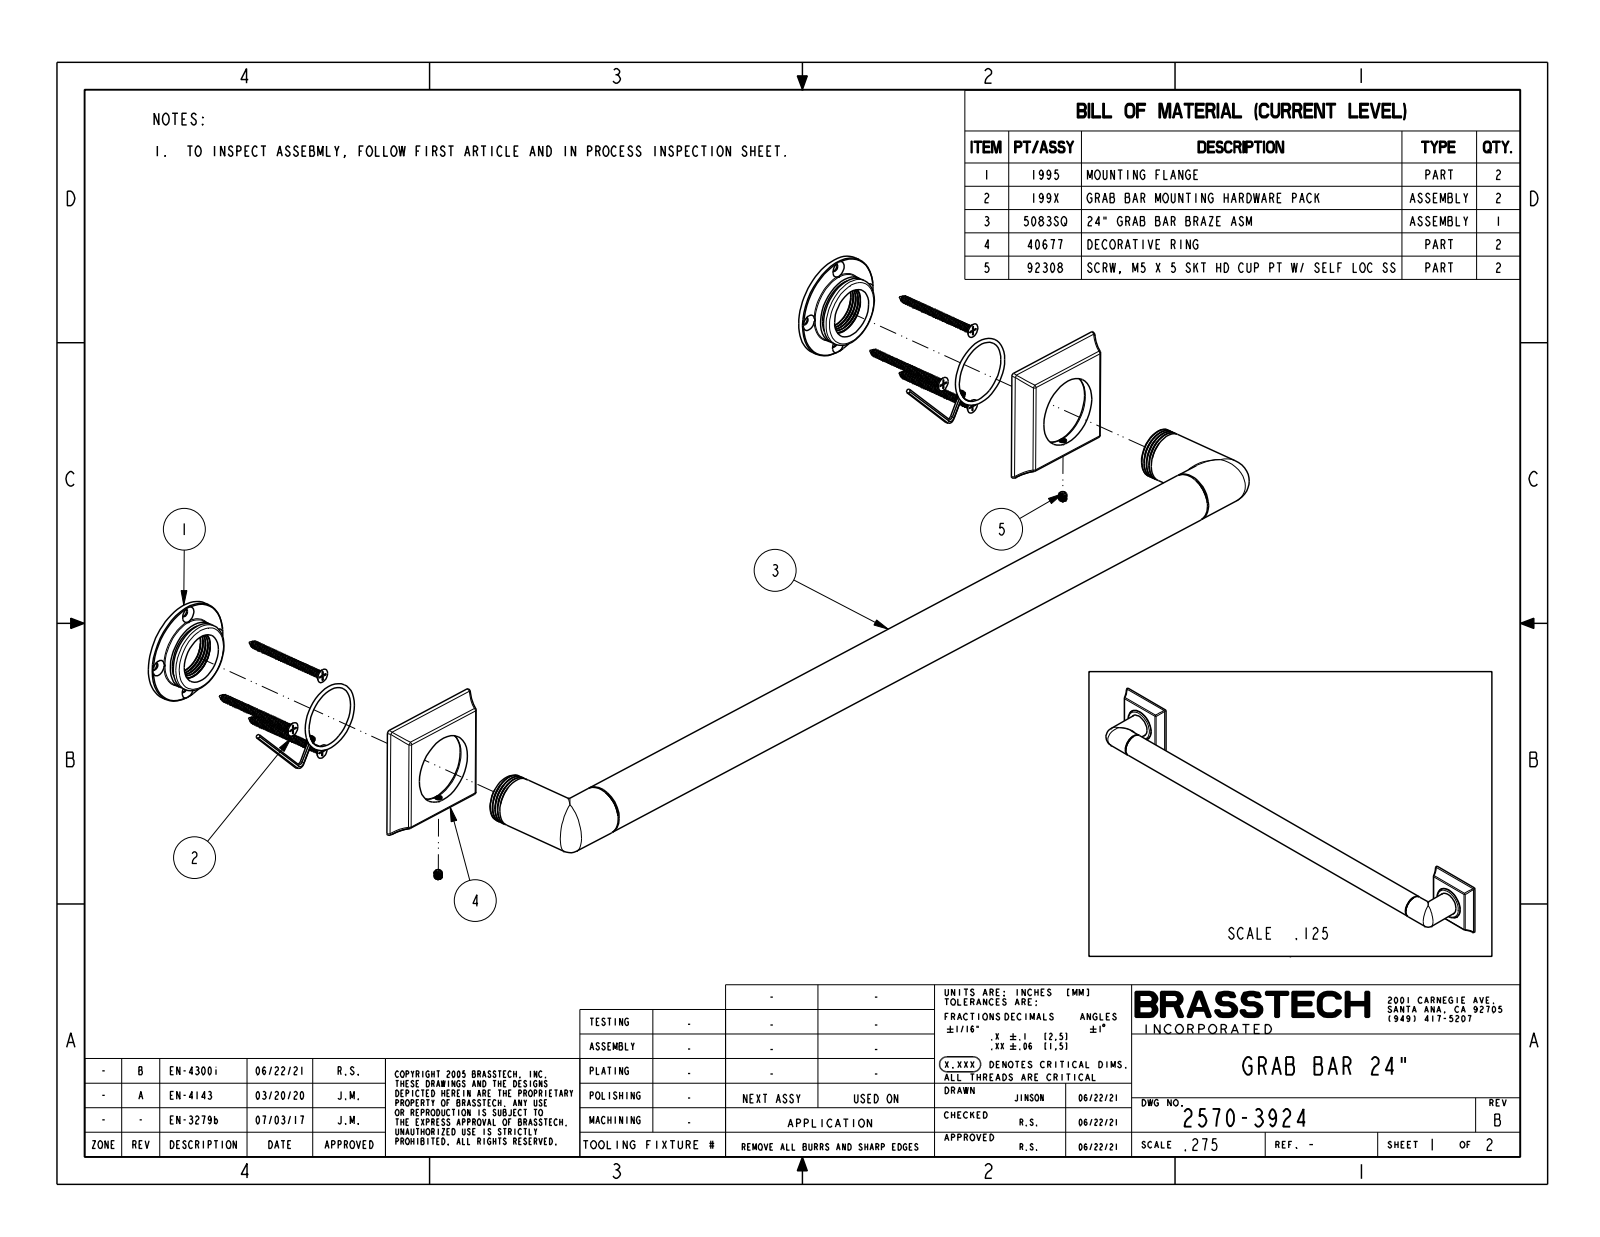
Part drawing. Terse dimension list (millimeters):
name: 2570-3924
written by: CREO PARAMETRIC BY PTC INC, 2018400 (CONFIG_CONTROL_DESIGN)
unit: mm
bodies: 1 solid, 88 faces (6 planar, 38 cylindrical, 44 other)
size: 685.8 × 76.2 × 70
volume: 675 500 mm³; area: 94 640 mm²
bosses: 3× ⌀31.8, 2× ⌀44.5
rounds: 6× R1.5, 6× R3.2, 6× R34.3
face distances: 13.3, 15.2, 1.9
